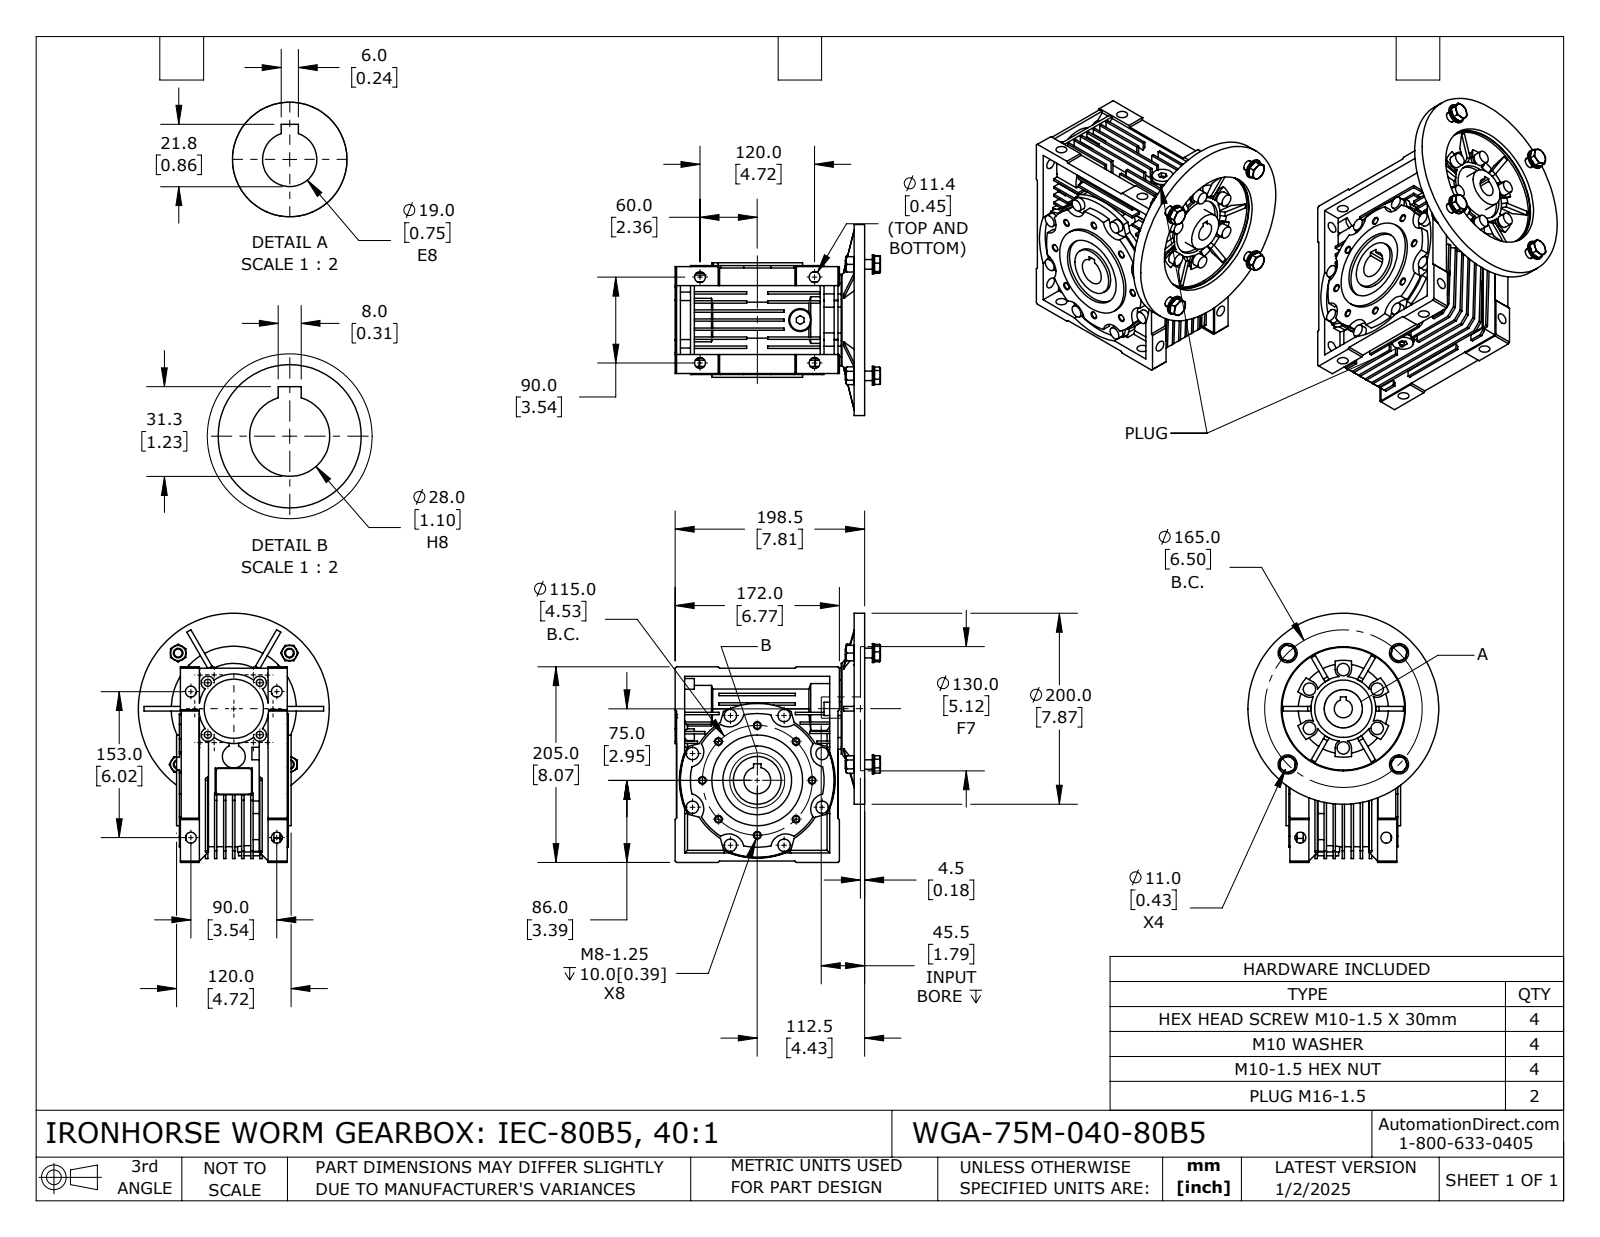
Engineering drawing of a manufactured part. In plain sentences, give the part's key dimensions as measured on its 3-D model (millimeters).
The part is named "WGA-75M-040-80B5". Its 3-D file was written by "SolidWorks 2024 (CONFIG_CONTROL_DESIGN)". It is 20 solids with 1447 faces: 790 planar, 439 cylindrical and 218 other. Overall it measures 261 by 214.93 by 200 millimeters. Its volume is 3 051 000 cubic millimeters and its surface area 536 406 square millimeters. Round holes: 8 of diameter 6.65, 8 of diameter 11.38, 4 of diameter 7.45, 4 of diameter 8.5, 4 of diameter 10, 4 of diameter 10.5, 4 of diameter 11, 2 of diameter 14.5, 1 of diameter 19, 1 of diameter 20, 1 of diameter 28, 1 of diameter 39. Round bosses or shafts: 14 of diameter 13, 4 of diameter 20, 4 of diameter 16, 3 of diameter 24, 2 of diameter 95, 2 of diameter 22, 2 of diameter 15.8, 2 of diameter 13.7. Partial cylindrical surfaces (rounded edges, fillets, slot ends): 10 of radius 7, 8 of radius 16, 6 of radius 8.5, 4 of radius 2.5, 1 of radius 33.99, 1 of radius 36, 1 of radius 36.5, 1 of radius 39. The main face-to-face distances are 9.5, 2.5, 19, 12, 7, 28.5, 16.5, 10, 27.75, 21.5. The hole center spacings are 44.01, 57.5, 81.32, 91.04, 106.25, 38.49, 54.44, 82.51.
